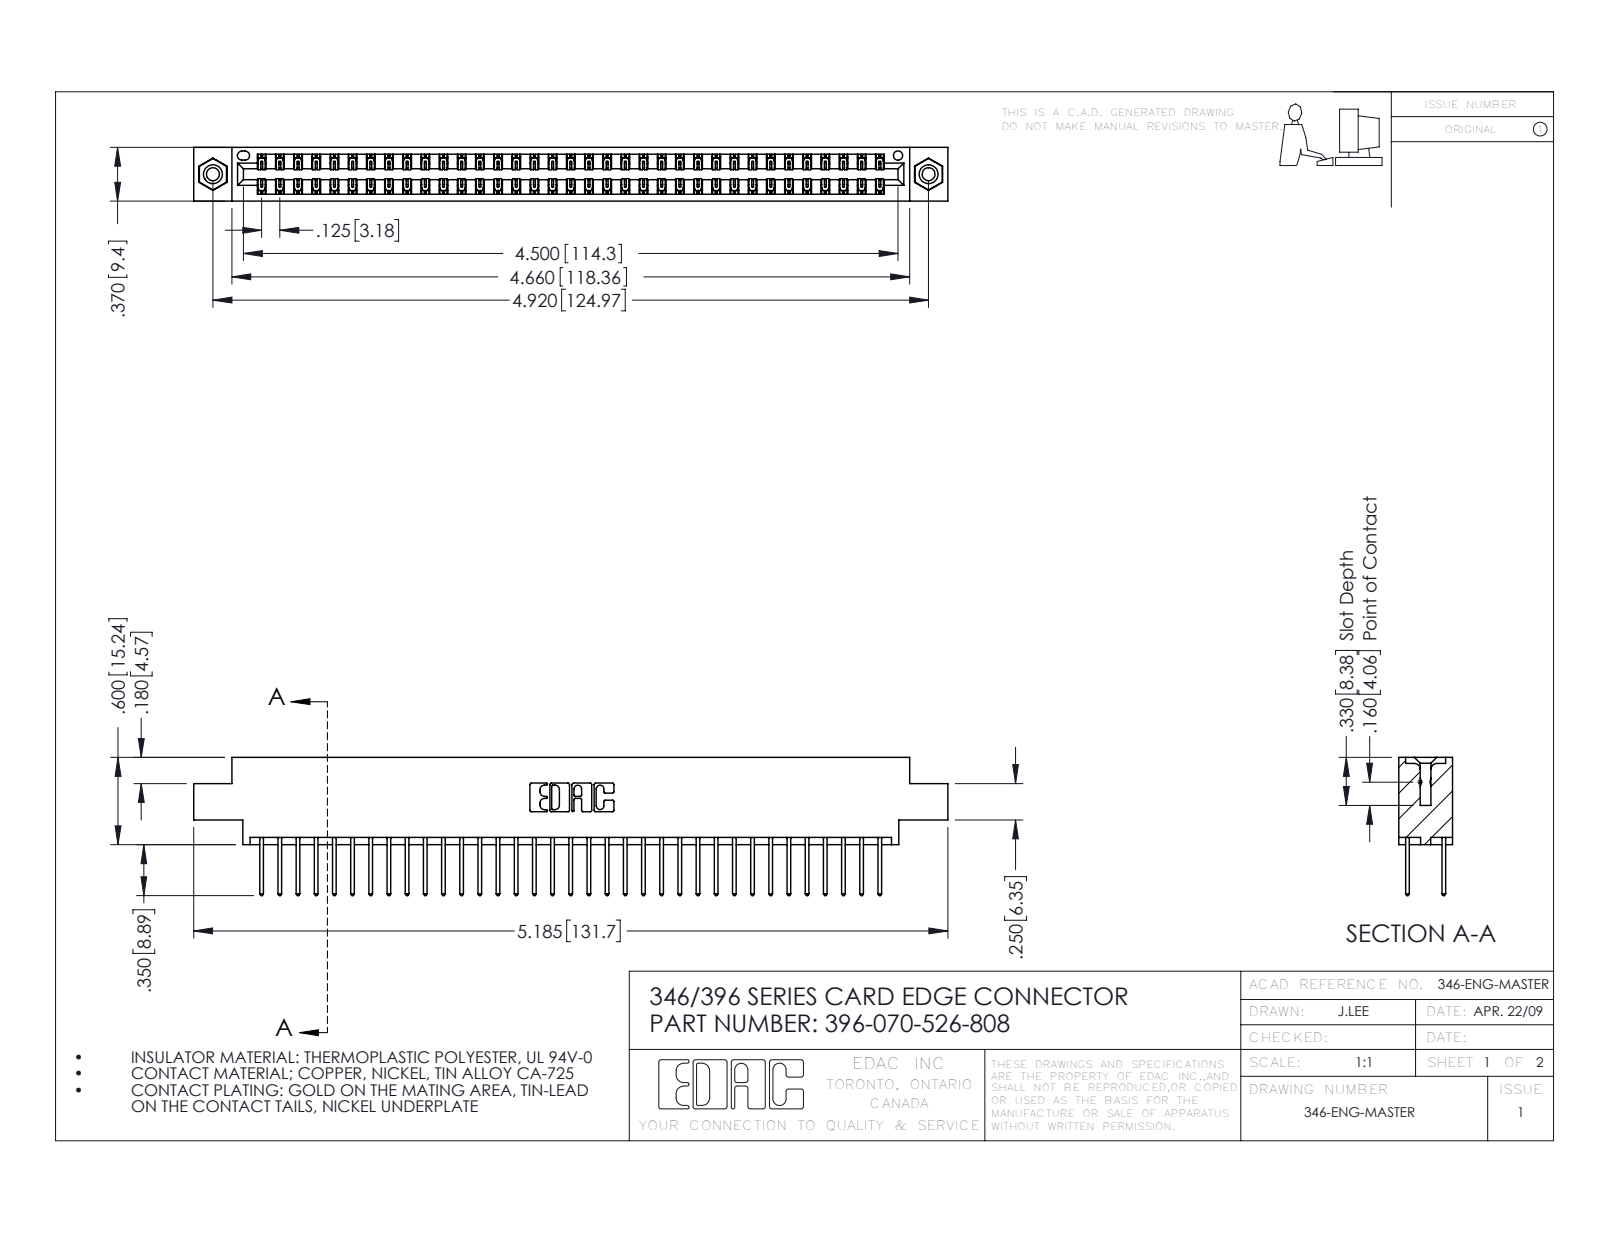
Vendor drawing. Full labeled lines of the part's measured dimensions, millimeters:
Part name (STEP PRODUCT): 396-070-526-808; 345-250-001_345-250-003-102; 345-292-001_345-293-126; 346 Part_0.170 Offset - 0.156 Dia-TI
STEP written by: SolidWorks 2016 (CONFIG_CONTROL_DESIGN)
Units: millimetres
Bodies: 73 solids, 3826 faces (2562 planar, 1248 cylindrical, 16 other)
Overall size (bounding box): 131.7 × 24.1 × 9.4
Volume: 12 700 mm³ · Surface area: 18 120 mm²
Round holes (diameter × count): ⌀2.3 ×2, ⌀3.2 ×2, ⌀4 ×2, ⌀1.6 ×1
Round bosses / shafts (diameter × count): ⌀3.9 ×2
Partial cylindrical surfaces — rounded edges, fillets, slot ends (radius × count): R0.2 ×105, R0.3 ×70, R0.3 ×22, R0.2 ×6, R0.8 ×6, R0.7 ×3, R0.4 ×2, R0.6 ×2
Main face-to-face distances: 1.2, 8.2, 6.4, 9.4, 1.8, 7.6, 0.6, 7, 5.6, 3.8
Hole centre spacings: 6.2, 119.7, 125
